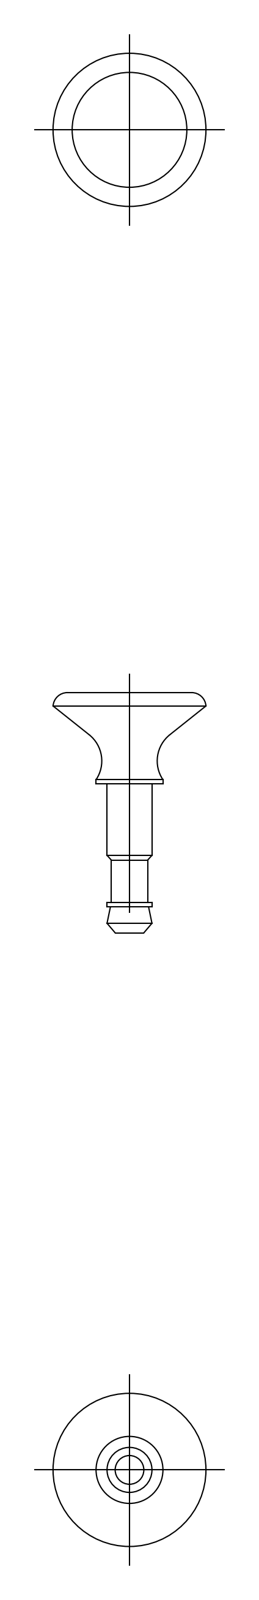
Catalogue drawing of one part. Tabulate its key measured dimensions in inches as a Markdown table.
| quantity | value |
| --- | --- |
| part name | plunger |
| STEP written by | CADfix (AUTOMOTIVE_DESIGN) |
| units | inches |
| bodies | 1 solid, 26 faces (0 planar, 0 cylindrical, 26 other) |
| overall size | 0.988 × 0.63 × 0.63 |
| volume | 0.055 in³ |
| surface area | 1.26 in² |
